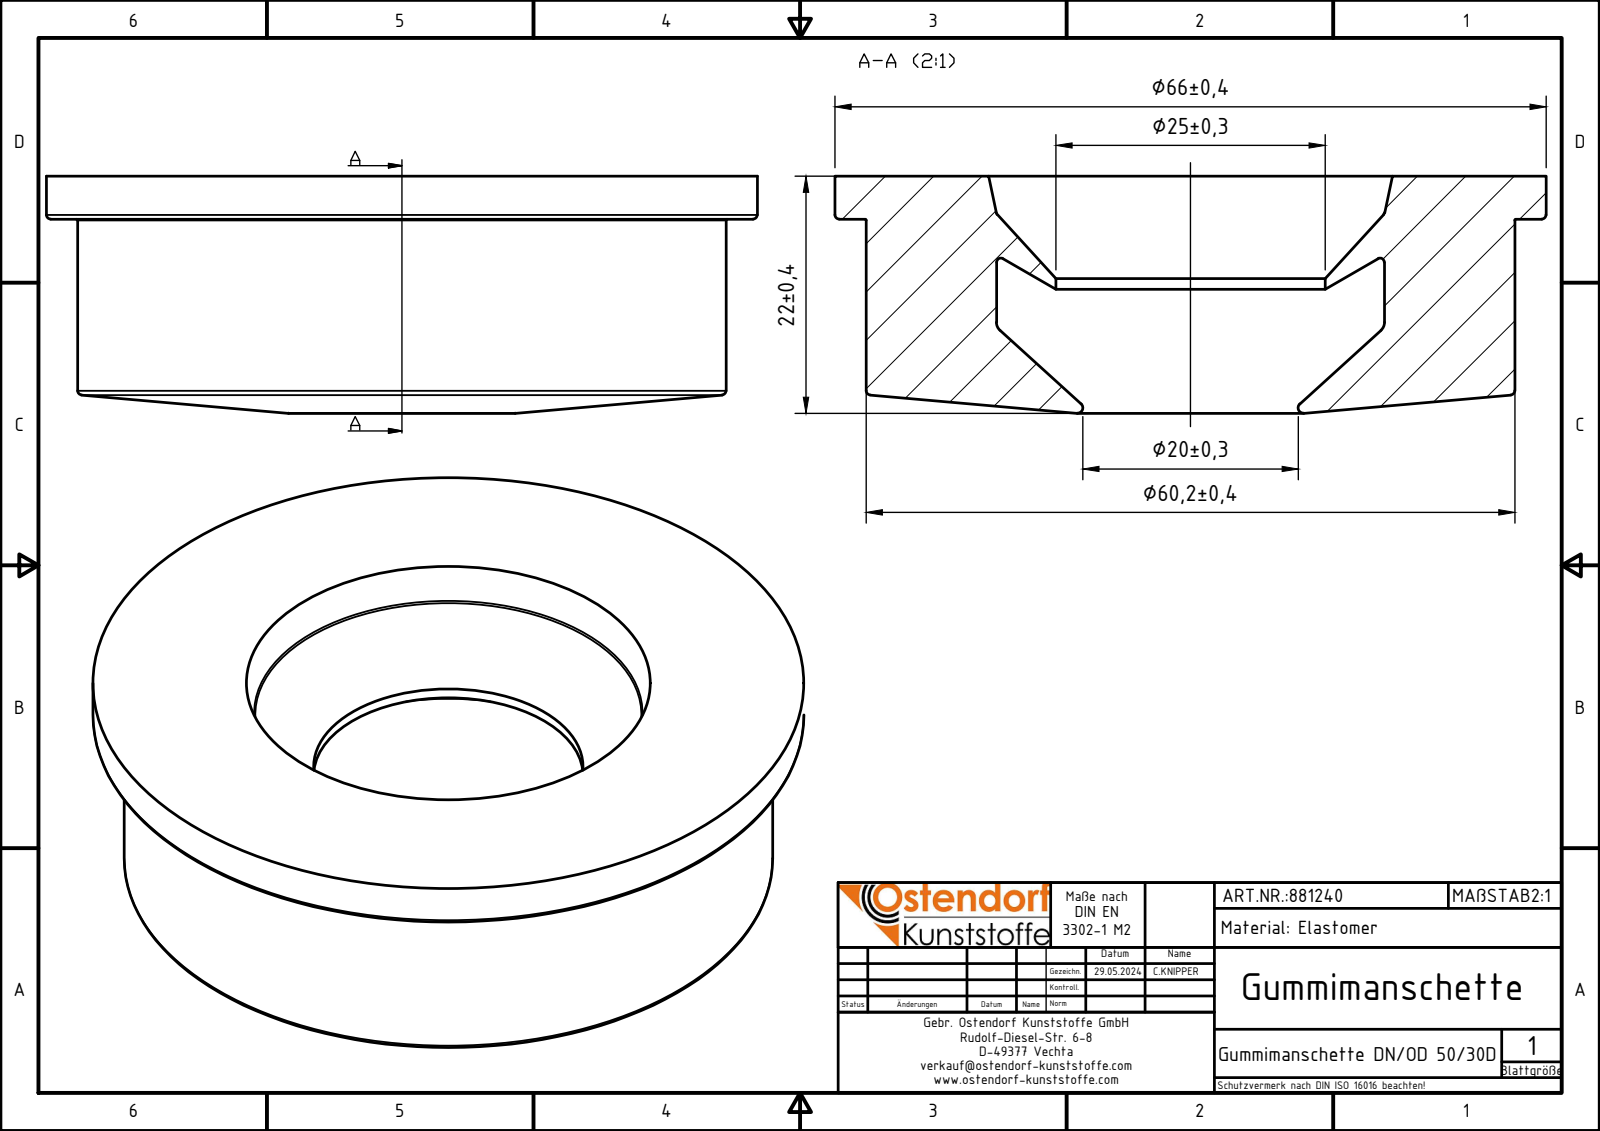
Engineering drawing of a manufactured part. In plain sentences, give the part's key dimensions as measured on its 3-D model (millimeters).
The part is named "881240z". Its 3-D file was written by "Autodesk Inventor 2024 (AUTOMOTIVE_DESIGN)". It is 1 solid with 18 faces: 2 planar, 4 cylindrical and 12 other. Overall it measures 66 by 66 by 22 millimeters. Its volume is 44 511 cubic millimeters and its surface area 12 826 square millimeters. Round holes: 1 of diameter 25, 1 of diameter 36.01. Round bosses or shafts: 1 of diameter 66, 1 of diameter 60.2. The main face-to-face distances are 4.
